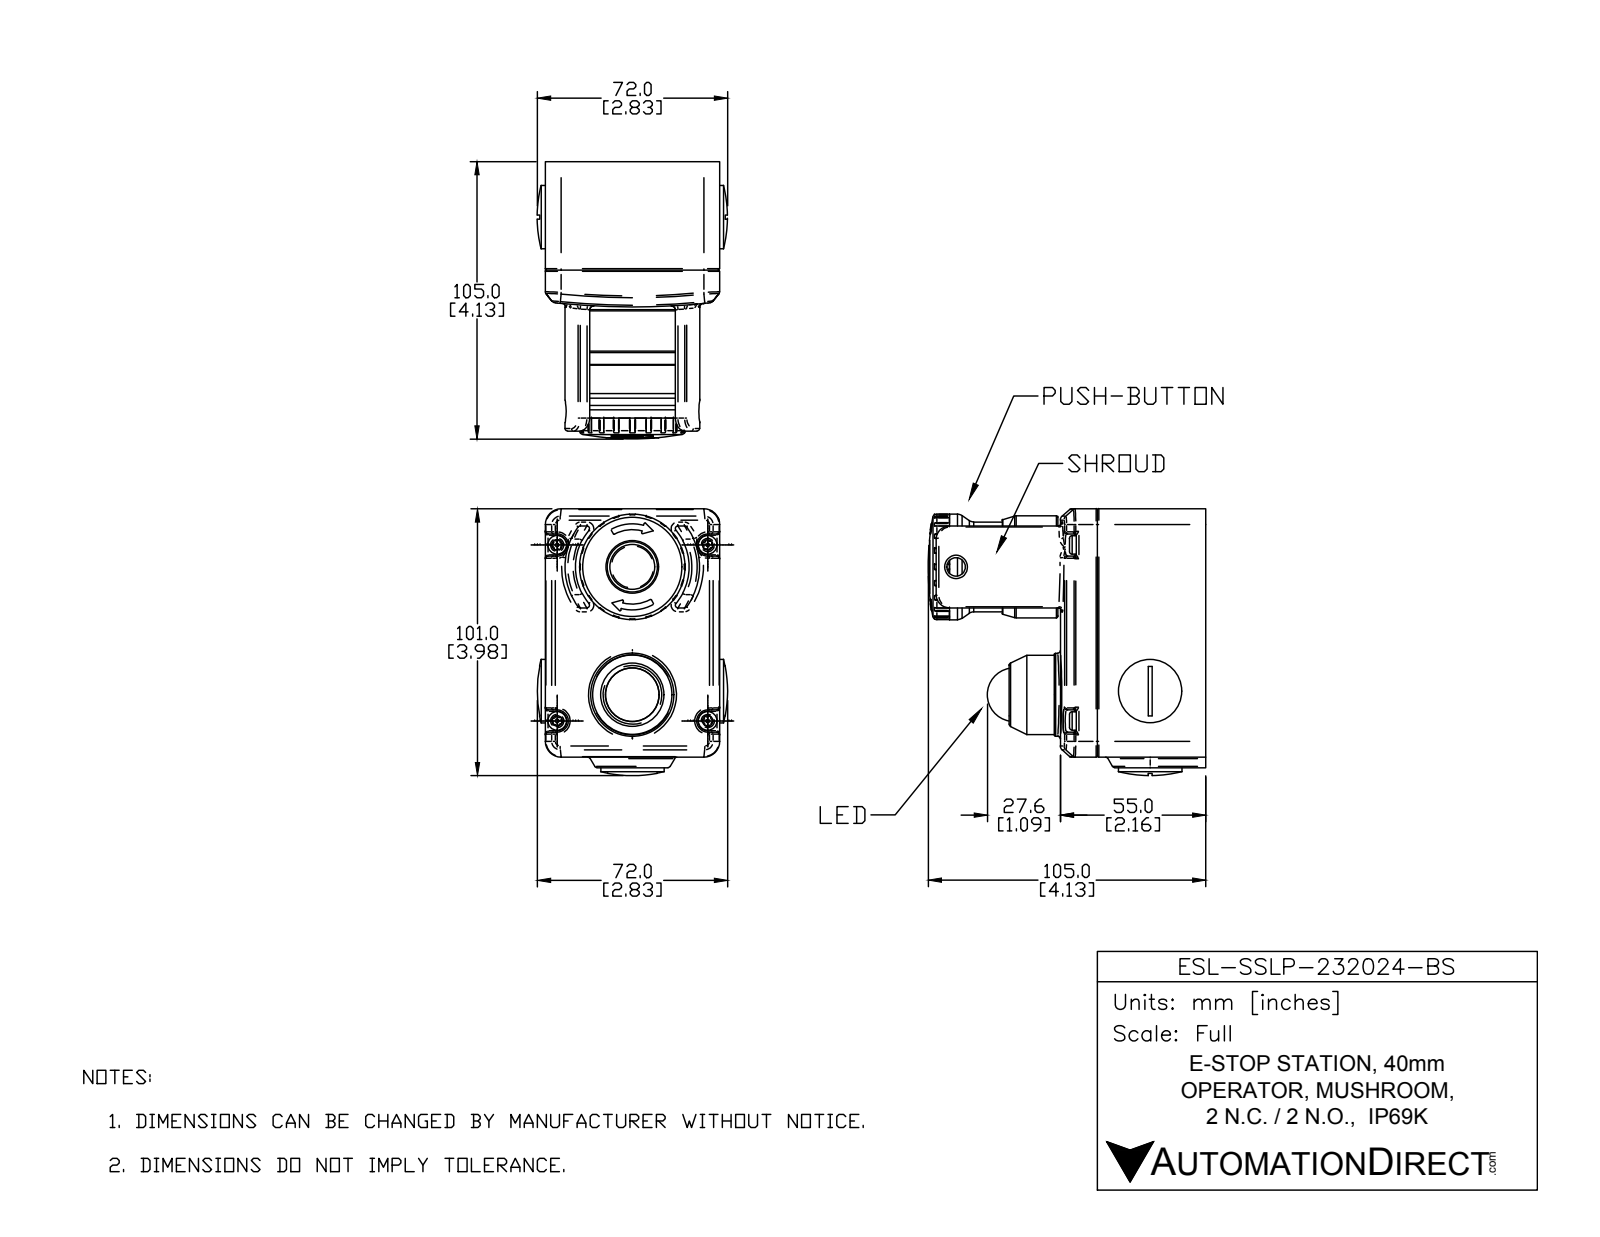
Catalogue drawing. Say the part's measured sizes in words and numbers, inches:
The part is named "ESL-SSLP-232024-BS". Its 3-D file was written by "SolidWorks 2016 (AUTOMOTIVE_DESIGN)". It is 13 solids with 797 faces: 227 planar, 287 cylindrical and 283 other. Overall it measures 4.134 by 3.976 by 2.834 inches. Its volume is 23.35 cubic inches and its surface area 112.8 square inches. Round holes: 4 of diameter 0.177, 1 of diameter 0.276, 1 of diameter 1.104, 1 of diameter 1.224, 1 of diameter 1.457. Round bosses or shafts: 4 of diameter 0.276, 4 of diameter 0.039, 2 of diameter 0.945, 1 of diameter 1.575, 1 of diameter 1.52, 1 of diameter 1.339, 1 of diameter 1.236, 1 of diameter 1.181. Partial cylindrical surfaces (rounded edges, fillets, slot ends): 80 of radius 0.004, 24 of radius 0.03, 14 of radius 0.02, 13 of radius 0.039, 6 of radius 0.059, 4 of radius 0.008, 4 of radius 0.165, 4 of radius 0.236. The main face-to-face distances are 1.614, 2.598, 2.205, 0.591, 3.858, 0.157, 3.701, 2.236, 0.622, 0.031. The hole center spacings are 1.235, 1.269, 2.126, 2.749, 2.807, 3.228, 3.865, 1.906.
